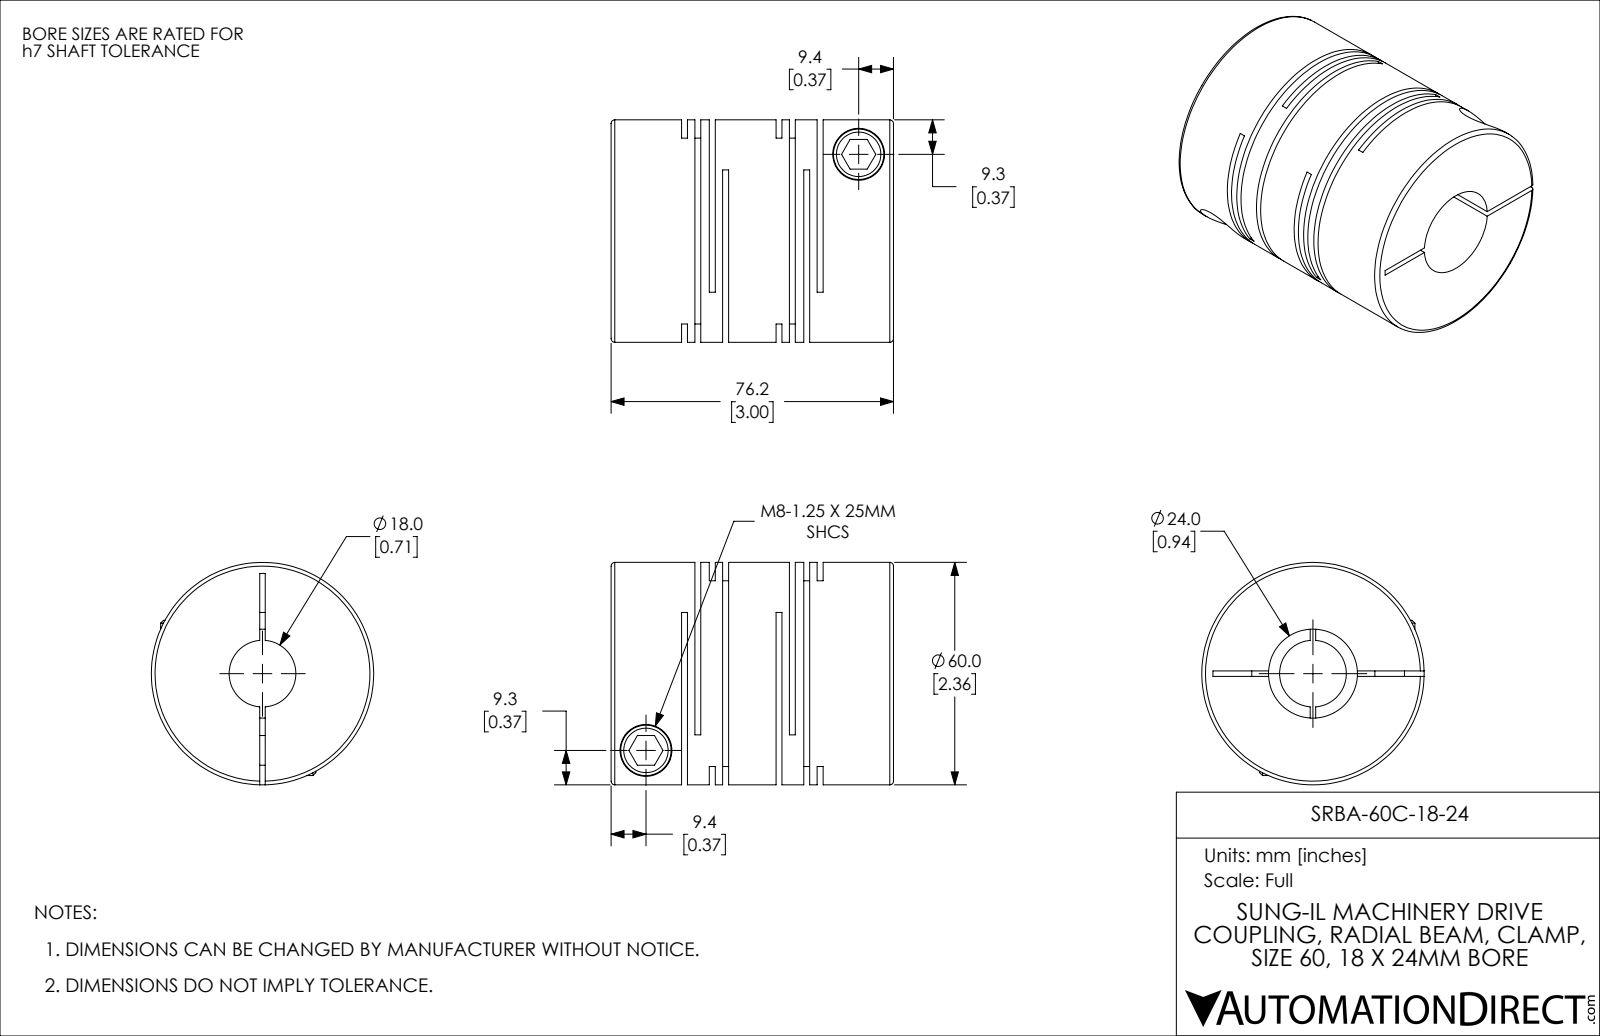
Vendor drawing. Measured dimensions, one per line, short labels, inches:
name: SRBA-60C-18-24
written by: SolidWorks 2021 (CONFIG_CONTROL_DESIGN)
unit: in
bodies: 1 solid, 115 faces (60 planar, 42 cylindrical, 13 other)
size: 3 × 2.362 × 2.362
volume: 9.479 in³; area: 88.97 in²
holes: 2× ⌀0.315, 2× ⌀0.551, 1× ⌀0.709, 1× ⌀0.945
bosses: 2× ⌀0.535, 1× ⌀2.362
face distances: 0.063, 0.142, 0.295, 1.004, 1.299, 1.067, 0.232, 0.941, 0.709, 0.079
